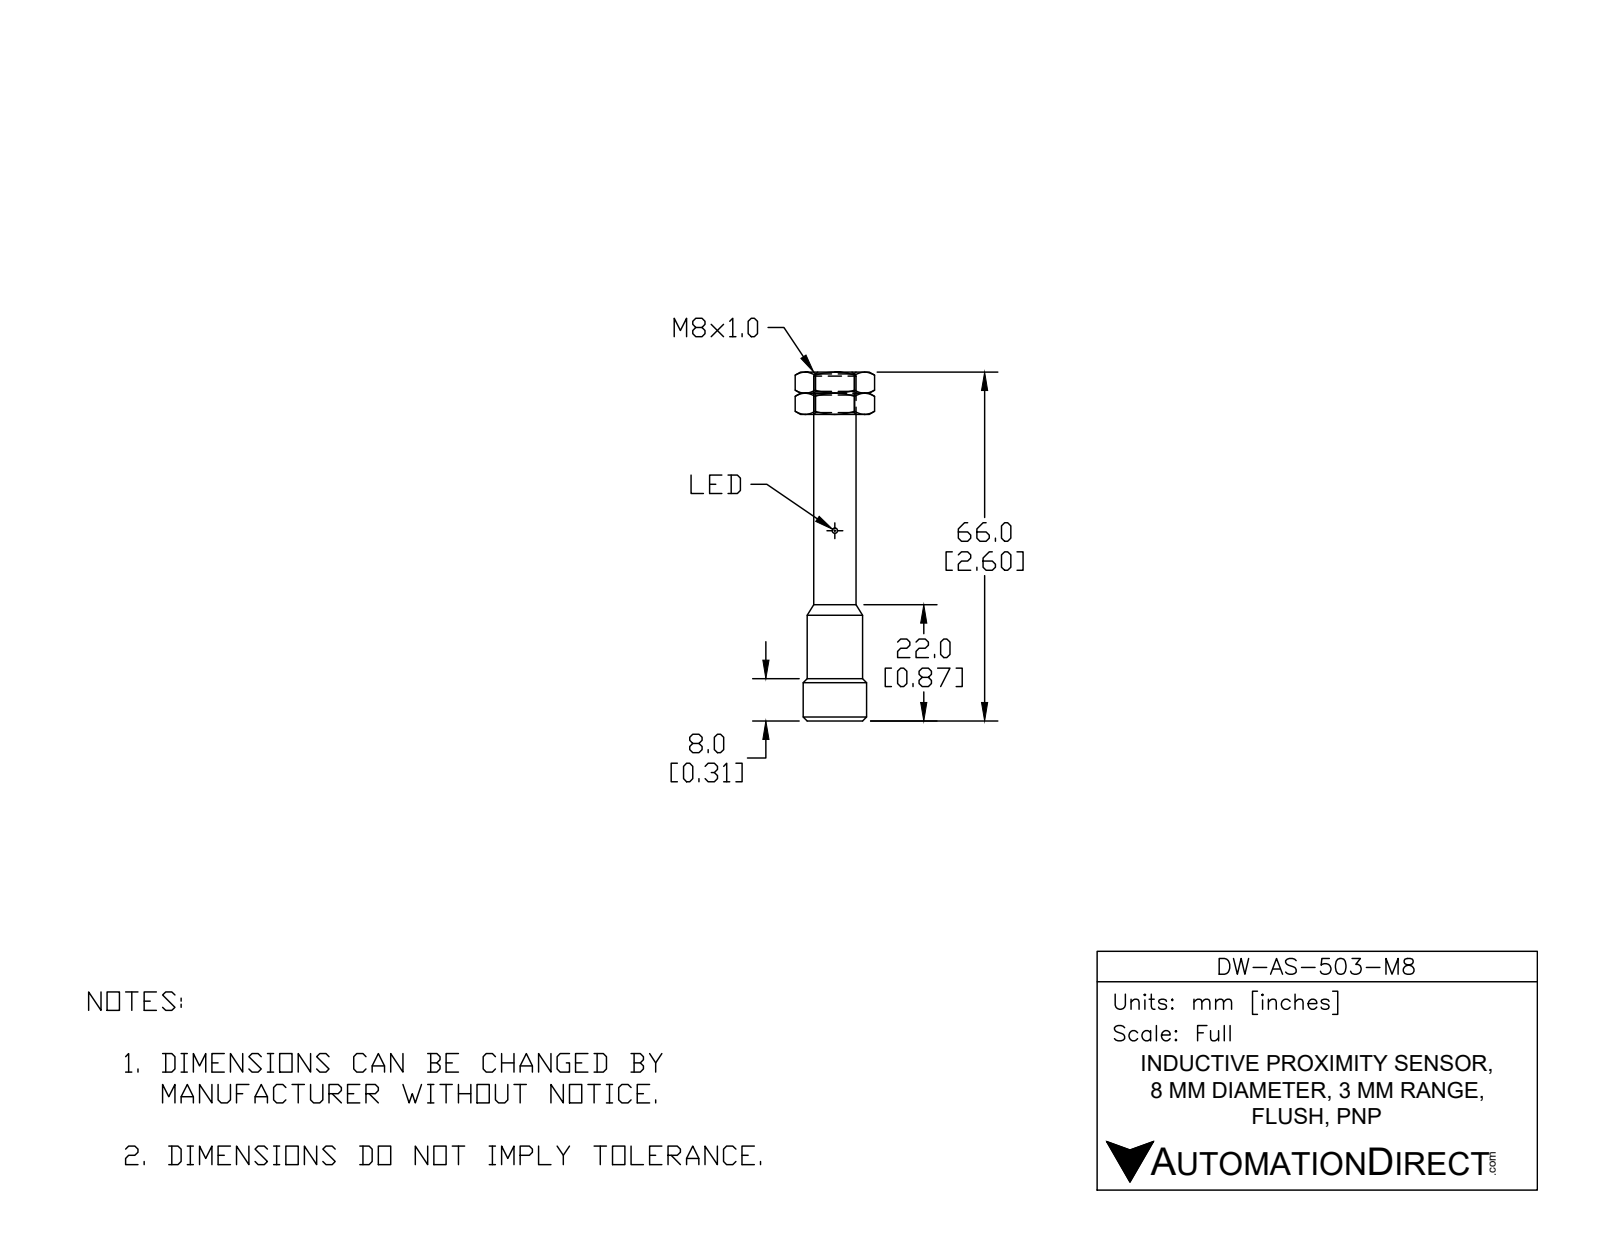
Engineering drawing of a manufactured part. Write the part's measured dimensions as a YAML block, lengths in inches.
part_name: "DW-AS-503-M8"
step_written_by: "SolidWorks 2017 (AUTOMOTIVE_DESIGN)"
units: inches
bodies: {solids: 1, faces: 35, planar: 10, cylindrical: 17, other: 8}
overall_size: [2.598, 0.472, 0.472]
volume: 0.23
surface_area: 3.709
round_holes:
  - {diameter: 0.12, count: 2}
round_bosses_or_shafts:
  - {diameter: 0.039, count: 4}
  - {diameter: 0.472, count: 1}
  - {diameter: 0.415, count: 1}
  - {diameter: 0.335, count: 1}
  - {diameter: 0.315, count: 1}
face_to_face_distances: [2.256, 2.598, 0.343, 1.811, 0.445, 0.787, 1.593, 0.218, 0.663, 1.005]
